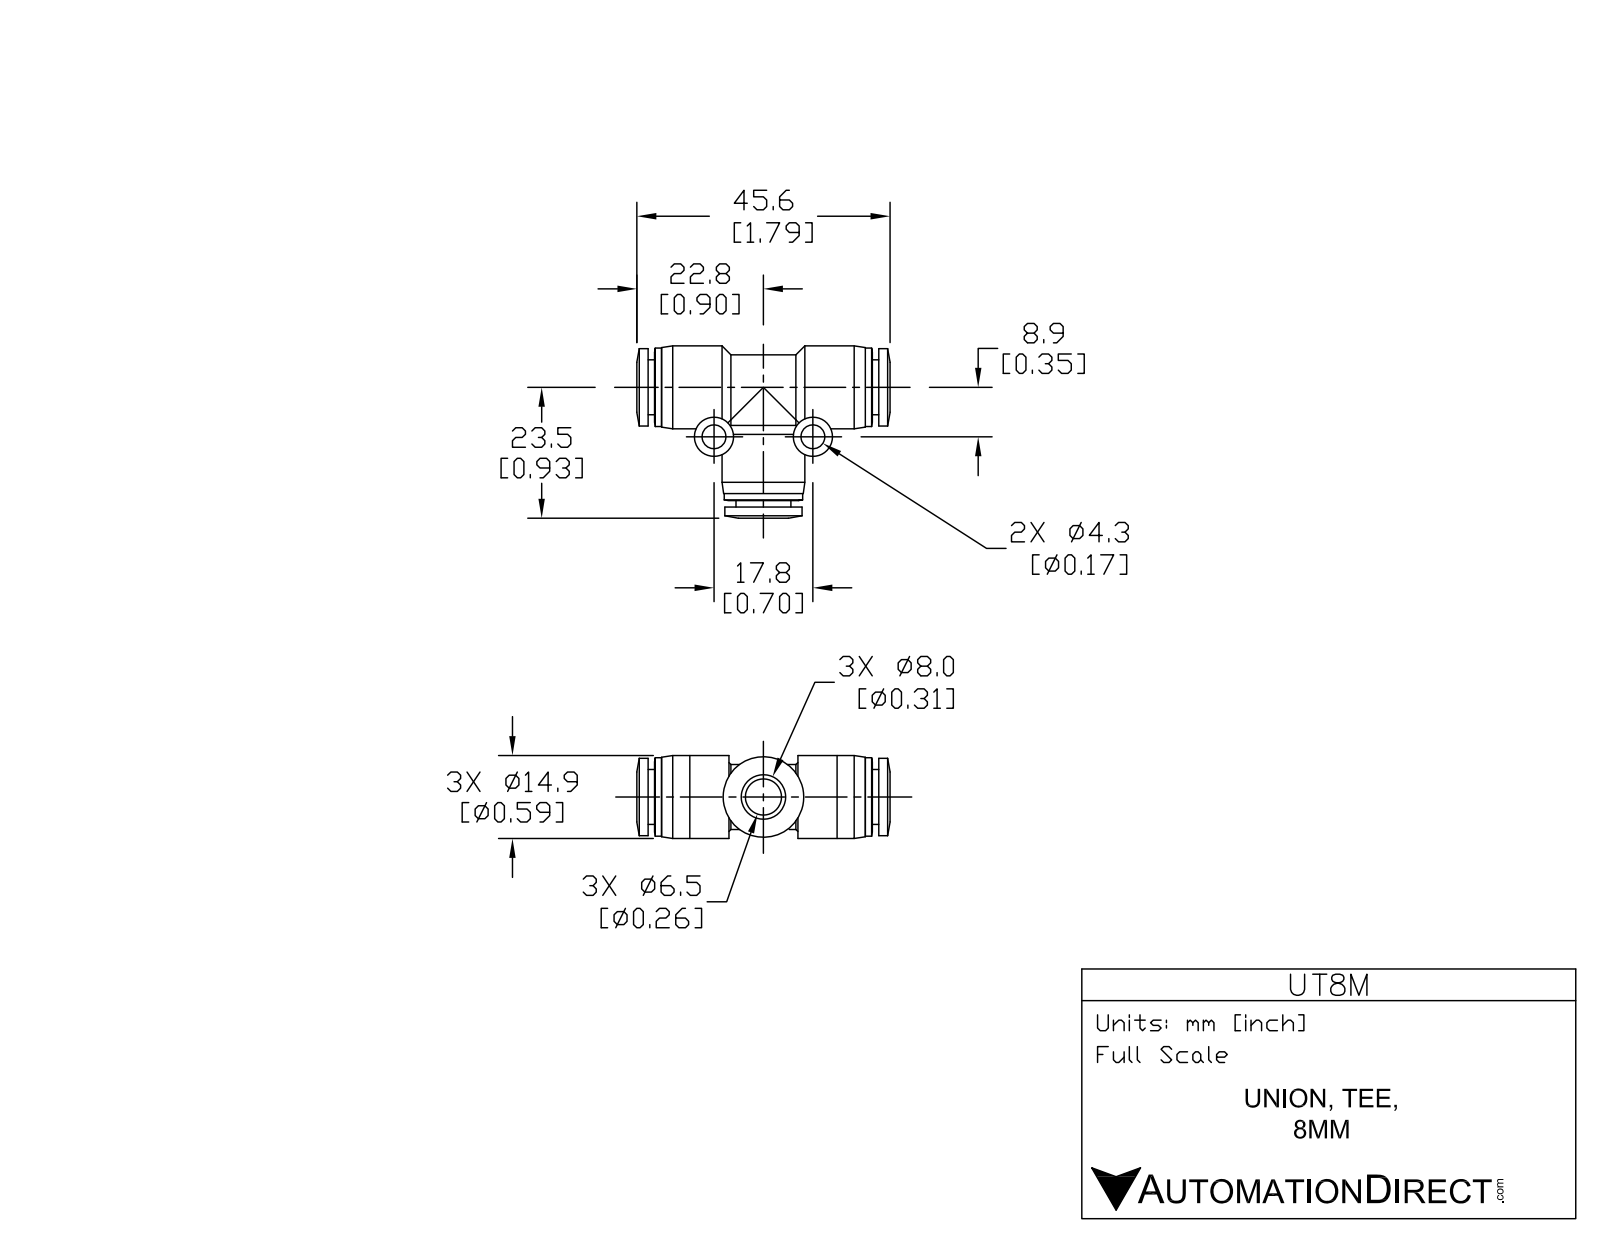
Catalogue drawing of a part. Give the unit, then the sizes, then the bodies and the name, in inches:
Units: inches
Overall size (bounding box): 1.78 × 1.22 × 0.583
Round holes (diameter × count): ⌀0.177 ×2, ⌀0.268 ×2, ⌀0.325 ×2
Round bosses / shafts (diameter × count): ⌀0.583 ×2, ⌀0.551 ×2, ⌀0.543 ×2, ⌀0.457 ×2, ⌀0.386 ×2, ⌀0.276 ×2
Main face-to-face distances: 0.045, 1.577, 1.622, 0.642, 0.596, 1.531, 0.583, 0.98, 0.935, 0.079
Hole centre spacings: 0.76
Volume: 0.399 in³ · Surface area: 9.229 in²
Bodies: 1 solid, 95 faces (19 planar, 46 cylindrical, 30 other)
Part name (STEP PRODUCT): UT8M
STEP written by: SolidWorks 2015 (AUTOMOTIVE_DESIGN)
